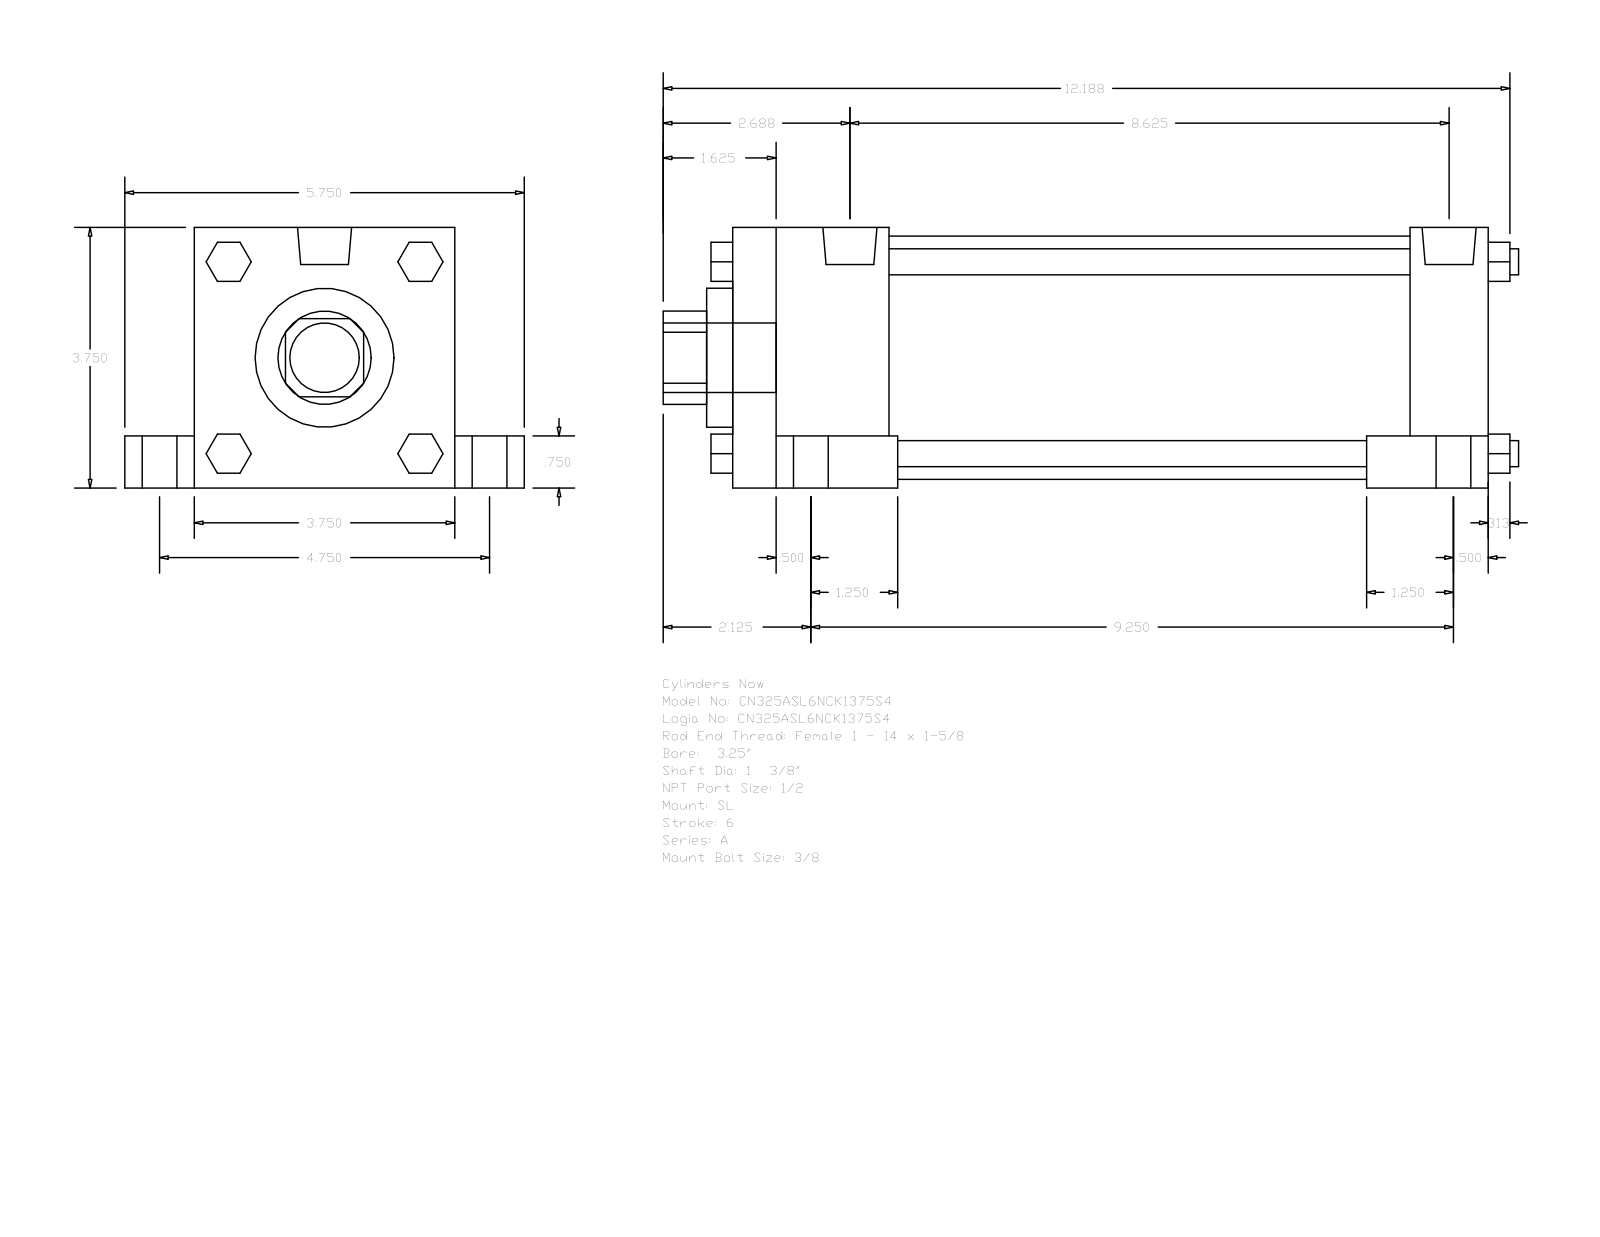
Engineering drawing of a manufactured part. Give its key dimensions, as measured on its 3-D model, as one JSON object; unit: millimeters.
{"part_name": "A_SL__0325_1.375", "step_written_by": "GSSL Pune (CONFIG_CONTROL_DESIGN)", "units": "millimeters", "bodies": {"solids": 0, "faces": 150, "planar": 114, "cylindrical": 36, "other": 0}, "overall_size": [312.74, 146.05, 95.25], "round_holes": [[34.92, 1], [50.8, 1], [88.9, 1]], "round_bosses_or_shafts": [[19.05, 4], [12.7, 4], [9.53, 4], [8.73, 4], [19.77, 2], [25.4, 1]], "partial_cylinders_radius": [[17.06, 1]], "face_to_face_distances": [95.24, 276.22, 25.41, 120.65, 19.05, 76.19, 15.87, 28.57, 57.15, 247.65]}
